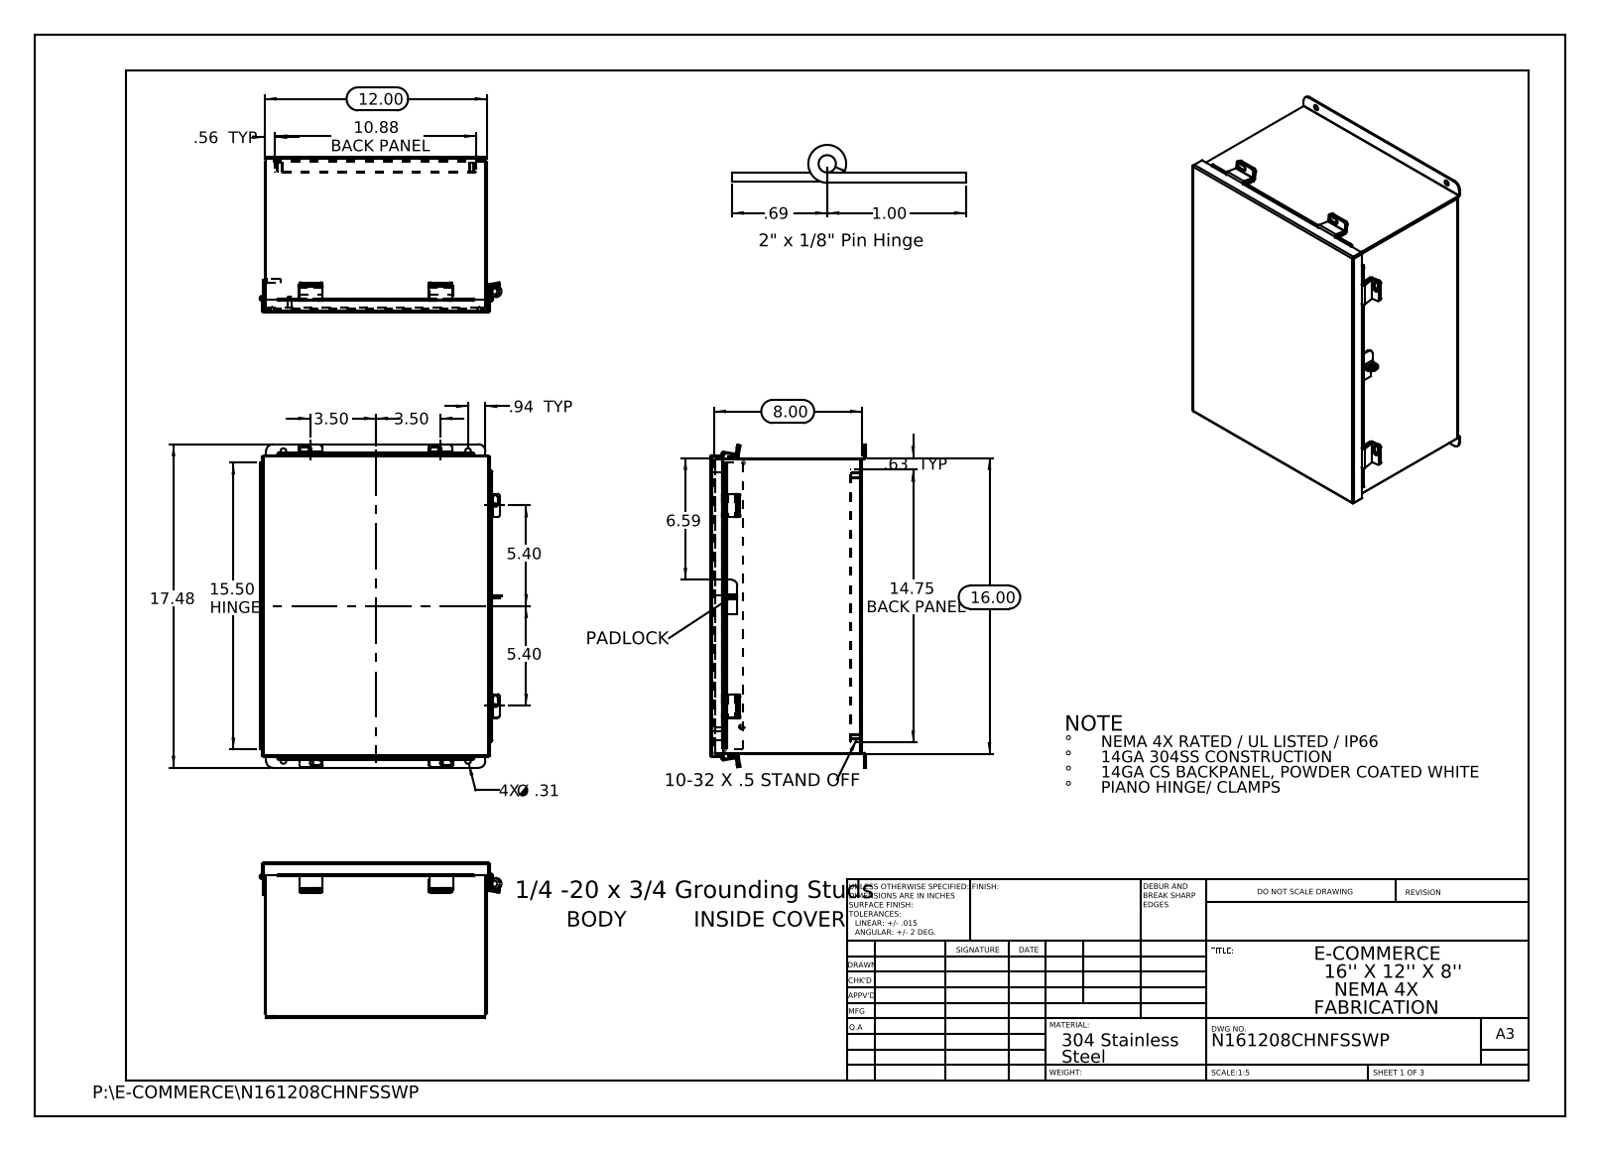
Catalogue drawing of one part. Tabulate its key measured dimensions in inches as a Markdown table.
| quantity | value |
| --- | --- |
| part name | N161208CHNFSSWP JIC Backpanel; HW-CLH-JH-20154; N161208CHNFSSWP HW-CD-S-25020-034; N161208CHNFSSWP (+8 more) |
| STEP written by | SolidWorks 2013 (CONFIG_CONTROL_DESIGN) |
| units | inches |
| bodies | 27 solids, 866 faces (539 planar, 307 cylindrical, 20 other) |
| overall size | 17.476 × 13.072 × 8.39 |
| volume | 83.73 in³ |
| surface area | 2 277 in² |
| round holes (diameter × count) | 0.25 × 10, 0.187 × 4, 0.312 × 4, 0.125 × 1, 0.125 × 1, 0.373 × 1, 0.375 × 1 |
| round bosses / shafts (diameter × count) | 0.313 × 4, 0.315 × 2, 0.236 × 2, 0.273 × 1, 0.25 × 1 |
| partial cylindrical surfaces (radius × count) | 0.125 × 24, 0.013 × 13, 0.009 × 12, 0.088 × 12, 0.133 × 12, 0.083 × 6, 0.1 × 6, 0.375 × 4 |
| main face-to-face distances | 0.075, 8.128, 11.925, 15.925, 8.053, 8.203, 7.628, 0.575, 0.5, 7.553 |
| hole center spacings | 1.315, 10.258, 15.427, 18.48, 7, 9.976, 10.375, 14.126 |
